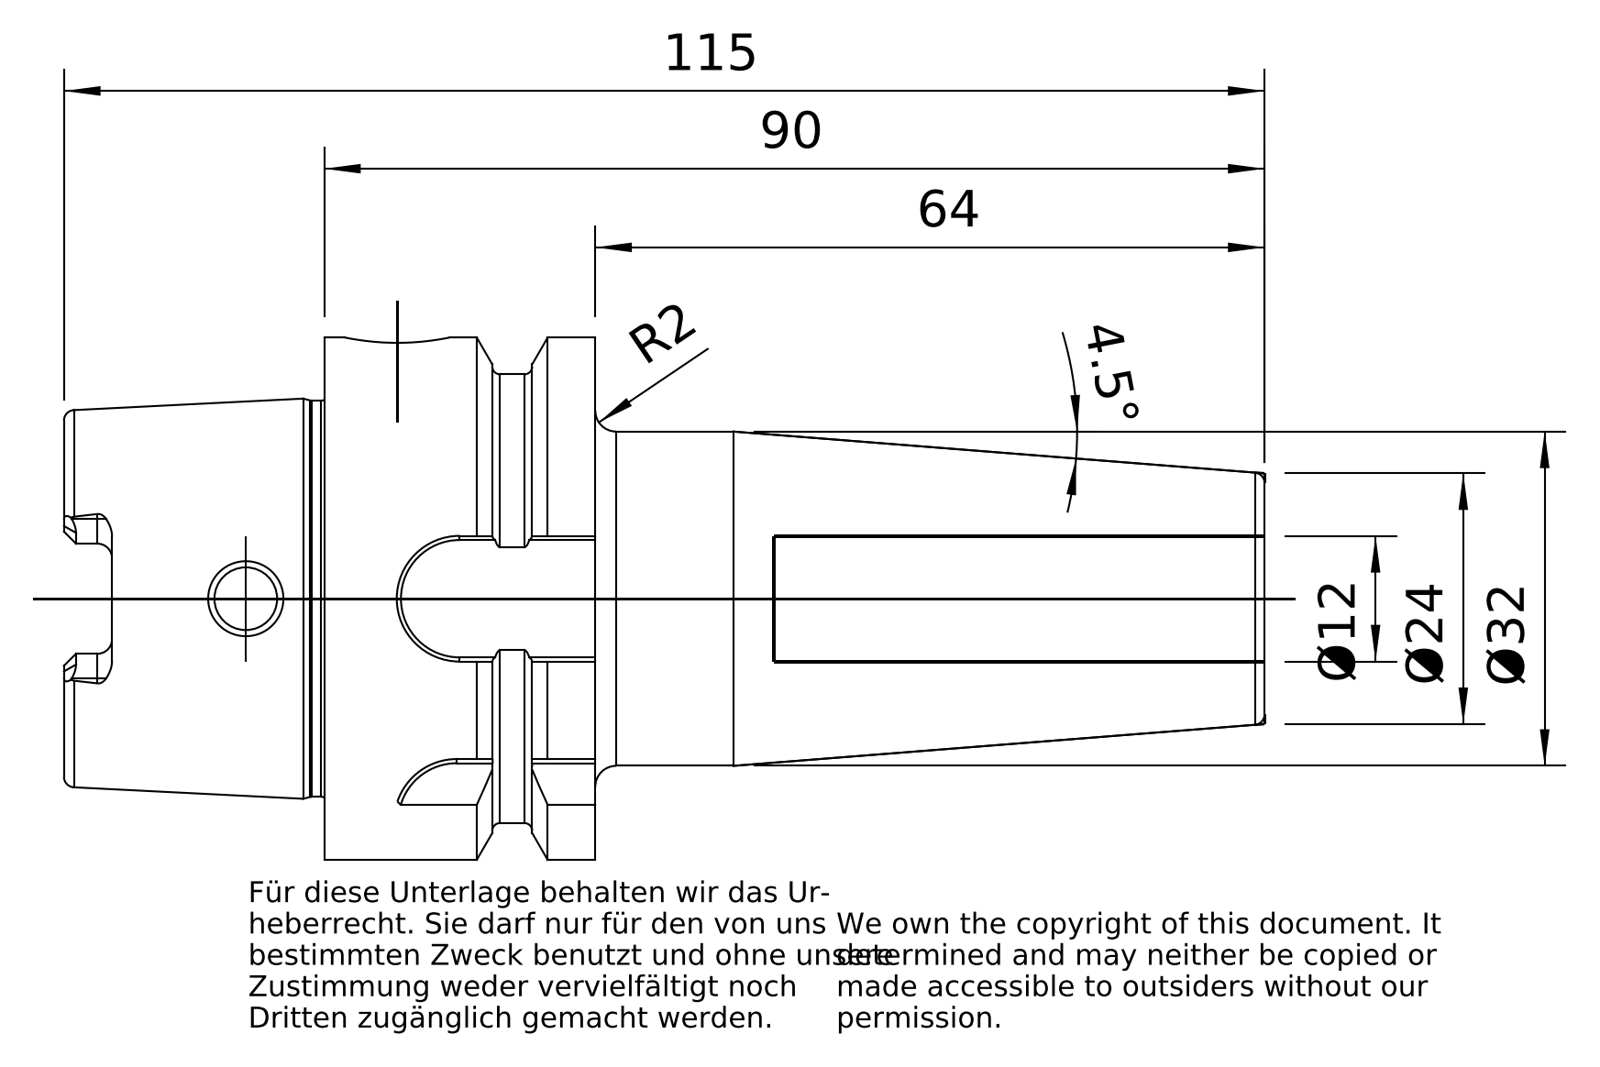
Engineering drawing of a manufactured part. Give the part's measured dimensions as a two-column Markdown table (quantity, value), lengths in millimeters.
| quantity | value |
| --- | --- |
| part name | A50-140-12 |
| STEP written by | PRO/ENGINEER BY PARAMETRIC TECHNOLOGY CORPORATION, 2010430 (CONFIG_CONTROL_DESIGN) |
| units | millimeters |
| bodies | 1 solid, 184 faces (63 planar, 49 cylindrical, 72 other) |
| overall size | 114.9 × 50 × 50 |
| volume | 85 772 mm³ |
| surface area | 22 433 mm² |
| round holes (diameter × count) | 6 × 1, 10 × 1, 12 × 1, 14 × 1, 16 × 1, 16.32 × 1, 16.5 × 1, 26.04 × 1, 32.08 × 1 |
| round bosses / shafts (diameter × count) | 50 × 1, 42.95 × 1, 37.91 × 1, 32 × 1 |
| partial cylindrical surfaces (radius × count) | 1.4 × 6, 2.38 × 4, 6 × 3, 6.02 × 1 |
| main face-to-face distances | 25.95, 90, 64.05, 24.9, 50.85, 114.9, 34.85, 9.95, 16, 80.05 |
